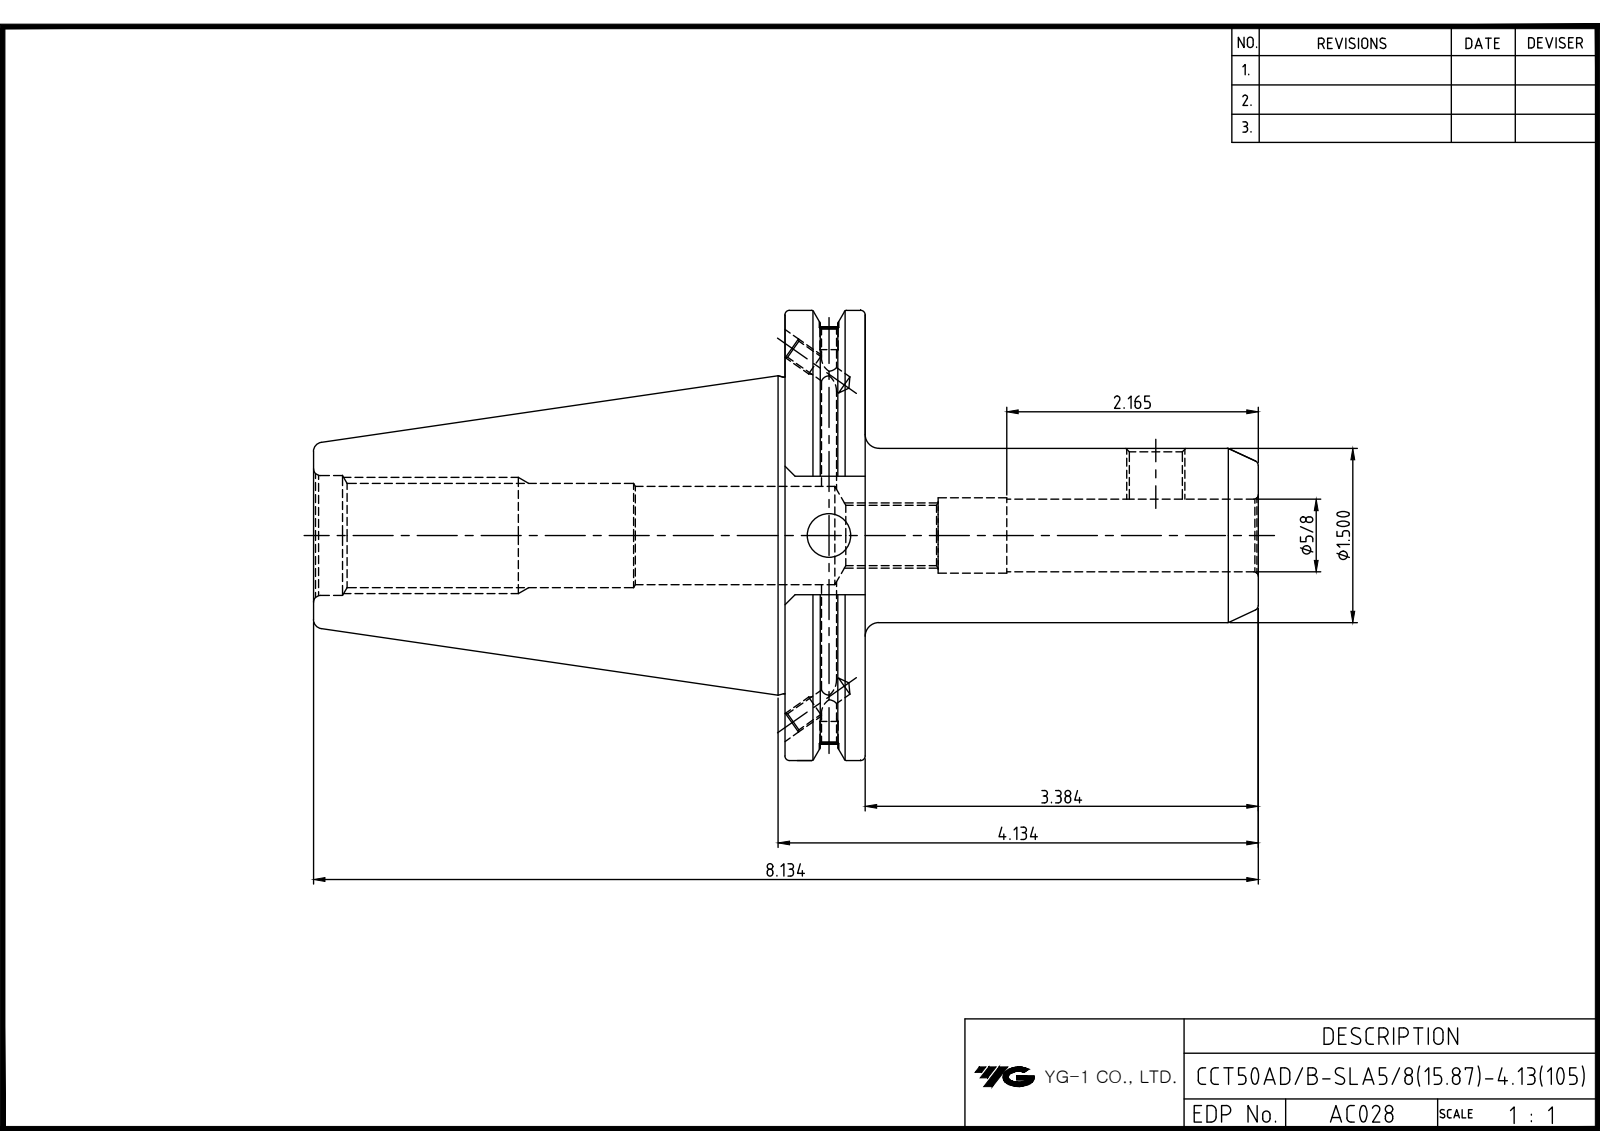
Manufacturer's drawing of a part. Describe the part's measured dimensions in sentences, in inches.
The part is named "LO-CCT50ADB-SLA15.875-105". Its 3-D file was written by "Autodesk Inventor 2025 (AUTOMOTIVE_DESIGN)". It is 1 solid with 92 faces: 40 planar, 27 cylindrical and 25 other. Overall it measures 8.134 by 3.875 by 3.728 inches. Its volume is 24.64 cubic inches and its surface area 92.22 square inches. Round holes: 2 of diameter 0.128, 2 of diameter 0.163, 2 of diameter 0.165, 2 of diameter 0.197, 1 of diameter 0.375, 1 of diameter 0.446, 1 of diameter 0.495, 1 of diameter 0.625, 1 of diameter 0.672, 1 of diameter 0.865, 1 of diameter 1.031. Round bosses or shafts: 1 of diameter 3.875, 1 of diameter 3.594, 1 of diameter 2.726, 1 of diameter 1.5. The main face-to-face distances are 0.691, 4.059, 4.075, 4.75, 8.134, 3.384, 2.875, 1.02, 0.016, 0.675.
